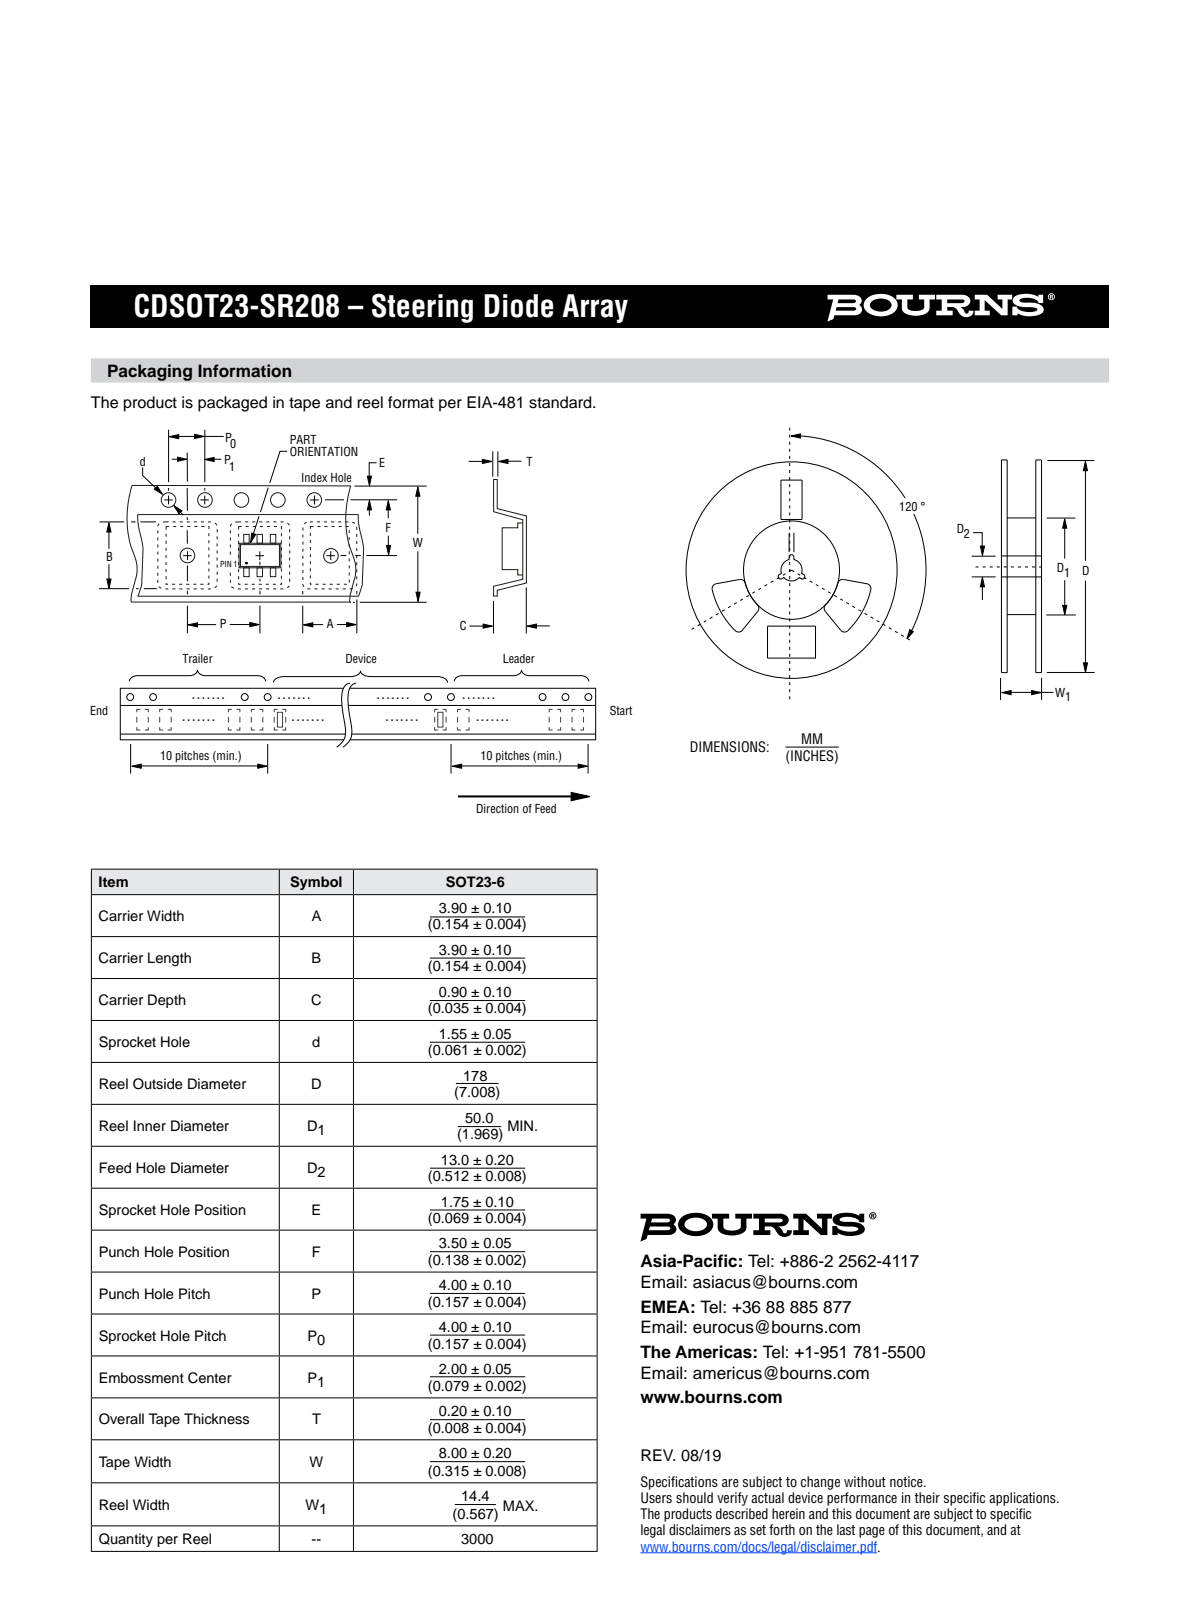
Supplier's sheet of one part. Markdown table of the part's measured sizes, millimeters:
| quantity | value |
| --- | --- |
| part name | CDSOT23-SR208 |
| STEP written by | PRO/ENGINEER BY PARAMETRIC TECHNOLOGY CORPORATION, 2010100 (CONFIG_CONTROL_DESIGN) |
| units | millimeters |
| bodies | 1 solid, 82 faces (58 planar, 24 cylindrical, 0 other) |
| overall size | 2.93 × 2.8 × 1.18 |
| volume | 5 mm³ |
| surface area | 27 mm² |
| partial cylindrical surfaces (radius × count) | 0.1 × 8 |
| main face-to-face distances | 1.1, 0.95, 2.92, 0.42, 0.53, 1.37, 1.9, 1.48, 2.32, 0.94 |
